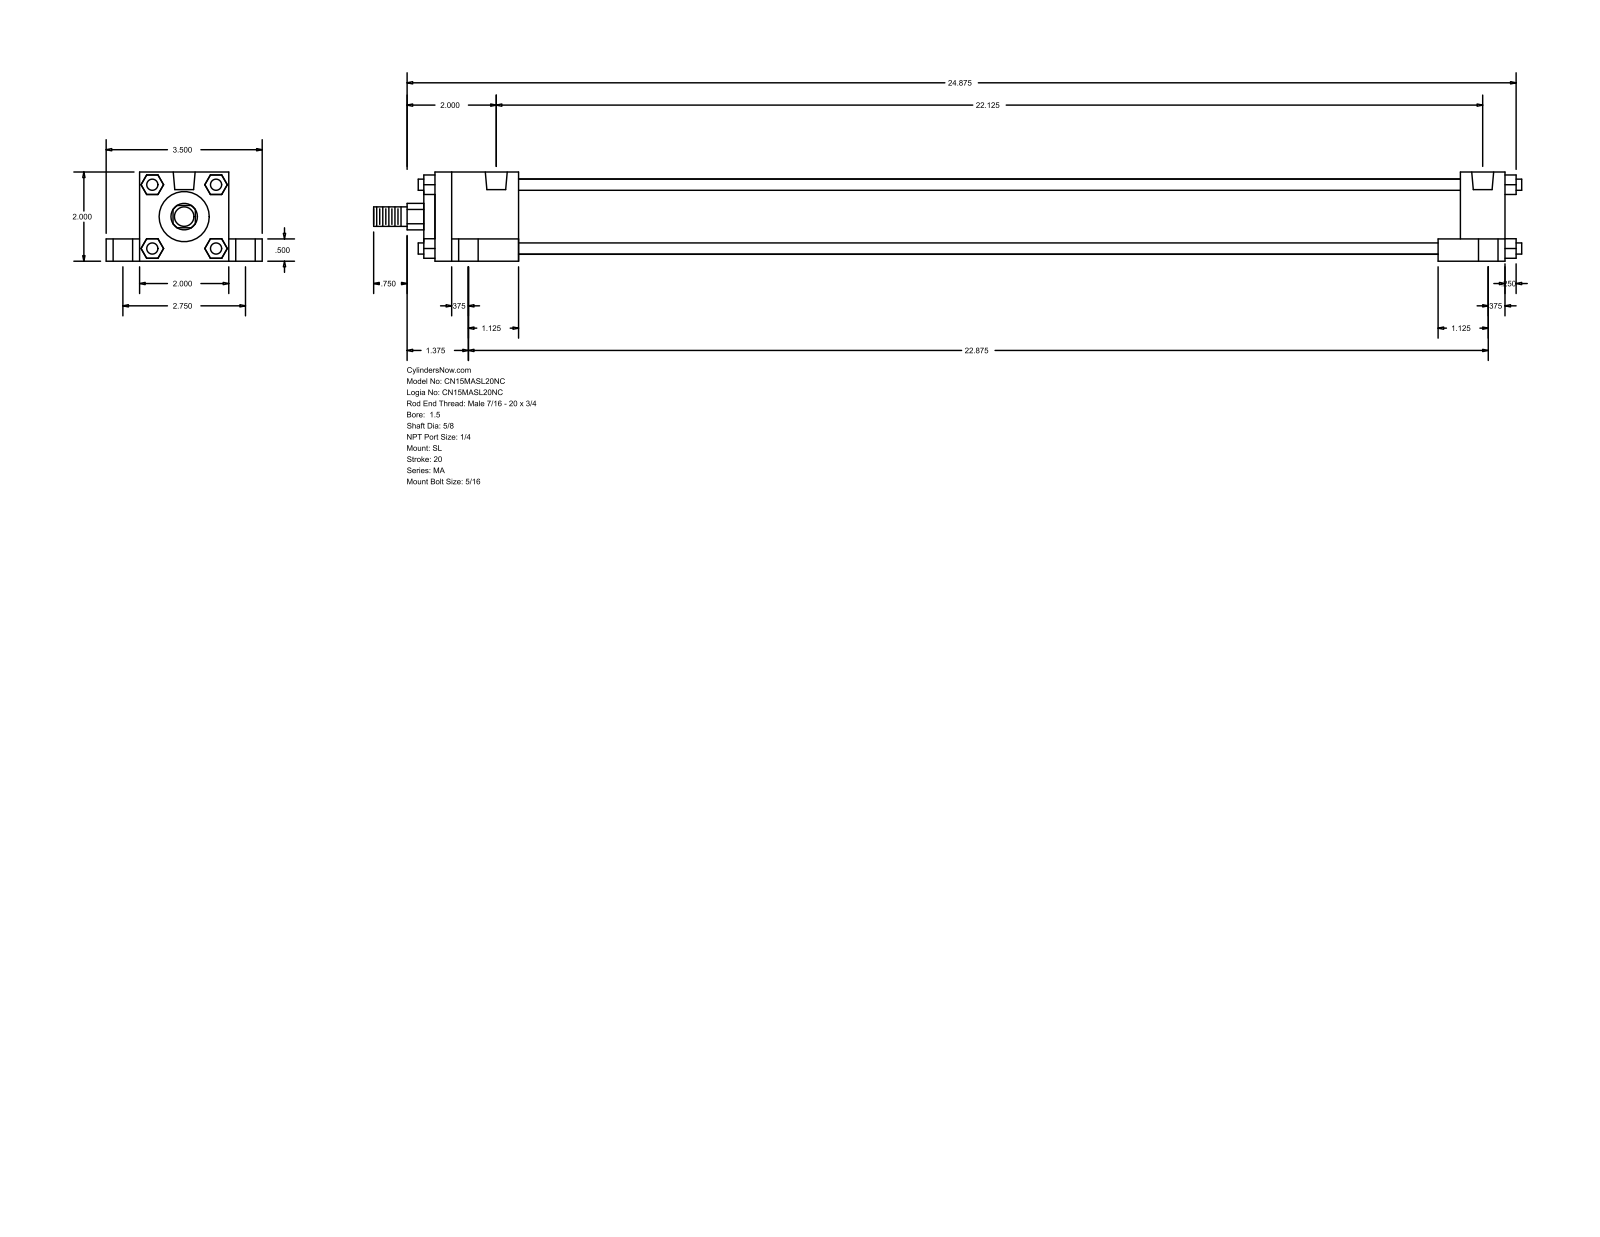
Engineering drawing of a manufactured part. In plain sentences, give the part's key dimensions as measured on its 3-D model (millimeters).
The part is named "MA_SL__0150_0.625". Its 3-D file was written by "GSSL Pune (CONFIG_CONTROL_DESIGN)". It is 0 solids with 148 faces: 112 planar, 36 cylindrical and 0 other. Overall it measures 654.05 by 88.9 by 50.8 millimeters. Round holes: 4 of diameter 7.94, 4 of diameter 11.11, 4 of diameter 17.46, 2 of diameter 12.49. Round bosses or shafts: 4 of diameter 6.35, 1 of diameter 42.93, 1 of diameter 28.57, 1 of diameter 15.88, 1 of diameter 11.11. Partial cylindrical surfaces (rounded edges, fillets, slot ends): 1 of radius 7.54. The main face-to-face distances are 50.8, 19.05, 38.1, 609.6, 69.85, 12.7, 9.52, 25.4, 6.35, 615.95. The hole center spacings are 35.06, 38.36, 69.84, 561.97, 566.23, 578.9, 581.03, 585.21.
